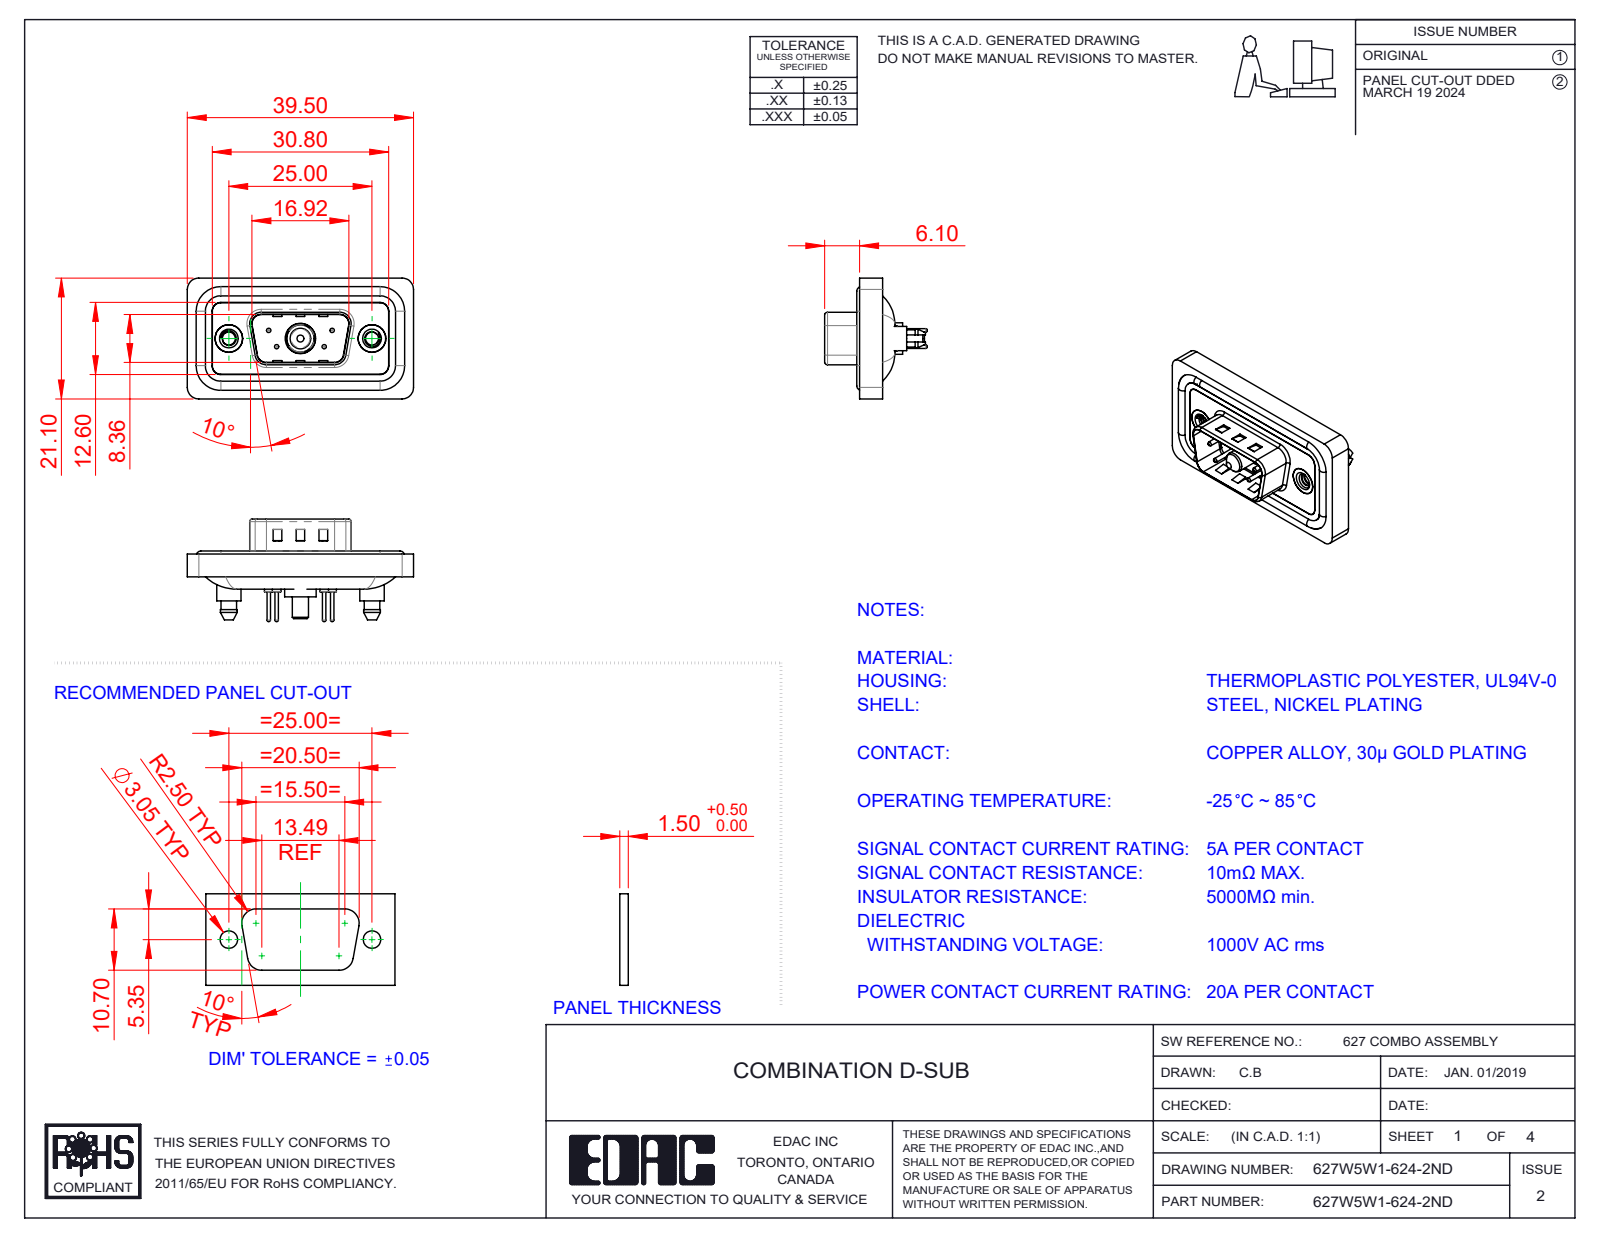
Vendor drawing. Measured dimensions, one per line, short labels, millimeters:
name: 627Combo Shell Front_09 Contacts; 627Combo Waterproof Housing_09 Contacts; 627Combo Threaded Boardlock_5; 627Combo Contact Row 1_24 (+6 more)
written by: SolidWorks 2023 (CONFIG_CONTROL_DESIGN)
unit: mm
bodies: 13 solids, 656 faces (199 planar, 295 cylindrical, 162 other)
size: 39.5 × 21.1 × 17.9
volume: 4 522 mm³; area: 7 277 mm²
holes: 4× ⌀0.75, 4× ⌀1.6, 4× ⌀2, 2× ⌀2.26, 2× ⌀4, 2× ⌀4.8, 2× ⌀5, 1× ⌀4.85, 1× ⌀5.3
bosses: 4× ⌀1.6, 4× ⌀1.5, 4× ⌀0.6, 2× ⌀5.4, 2× ⌀4.9, 2× ⌀4.25, 1× ⌀5.5, 1× ⌀5.2
rounds: 24× R1.5, 18× R2, 10× R1.6, 8× R0.5, 4× R0.25, 4× R0.6, 4× R0.65, 4× R0.9
face distances: 0.4, 1.1, 2.9, 1.6, 1.5, 3.1, 0.5, 2.5, 4, 0.8
hole spacings: 3.16, 5.72, 7.1, 12.5, 18.1, 4.39, 4.4, 8.31
